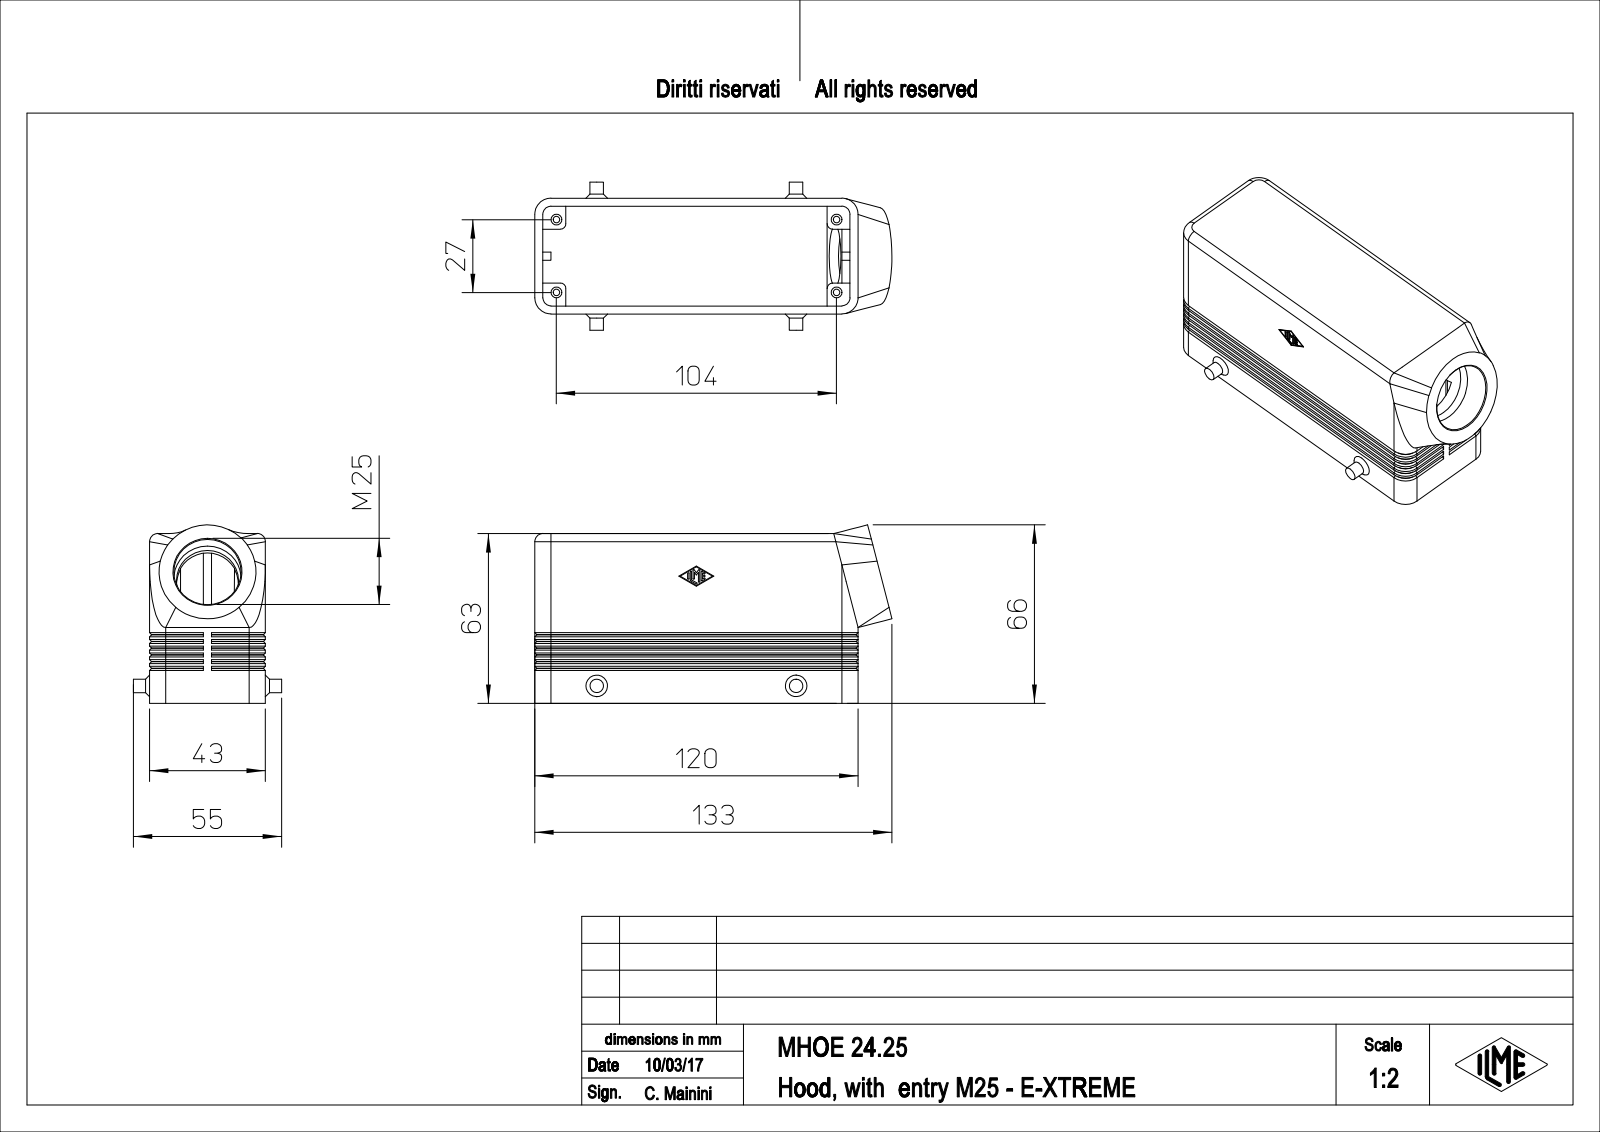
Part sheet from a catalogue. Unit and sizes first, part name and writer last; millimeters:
Units: millimetres
Overall size (bounding box): 132.59 × 66.25 × 55
Round holes (diameter × count): ⌀2.46 ×4, ⌀4 ×4, ⌀23 ×1, ⌀25 ×1
Round bosses / shafts (diameter × count): ⌀5 ×2
Partial cylindrical surfaces — rounded edges, fillets, slot ends (radius × count): R0.25 ×14, R3 ×7, R2 ×4, R5.3 ×4, R6 ×4, R1.5 ×1
Main face-to-face distances: 3, 40, 37, 43, 8.5, 11.5, 1.77, 5.3, 20, 105.5
Hole centre spacings: 27, 104, 107.45
Volume: 89 180 mm³ · Surface area: 50 684 mm²
Bodies: 1 solid, 408 faces (223 planar, 107 cylindrical, 78 other)
Part name (STEP PRODUCT): MHOE_24.25
STEP written by: PTC Creo Elements/Direct Modeling 19.0E 27-Jun-2016 (C) Parametric Technology GmbH (AUTOMOTIVE_DESIGN)
